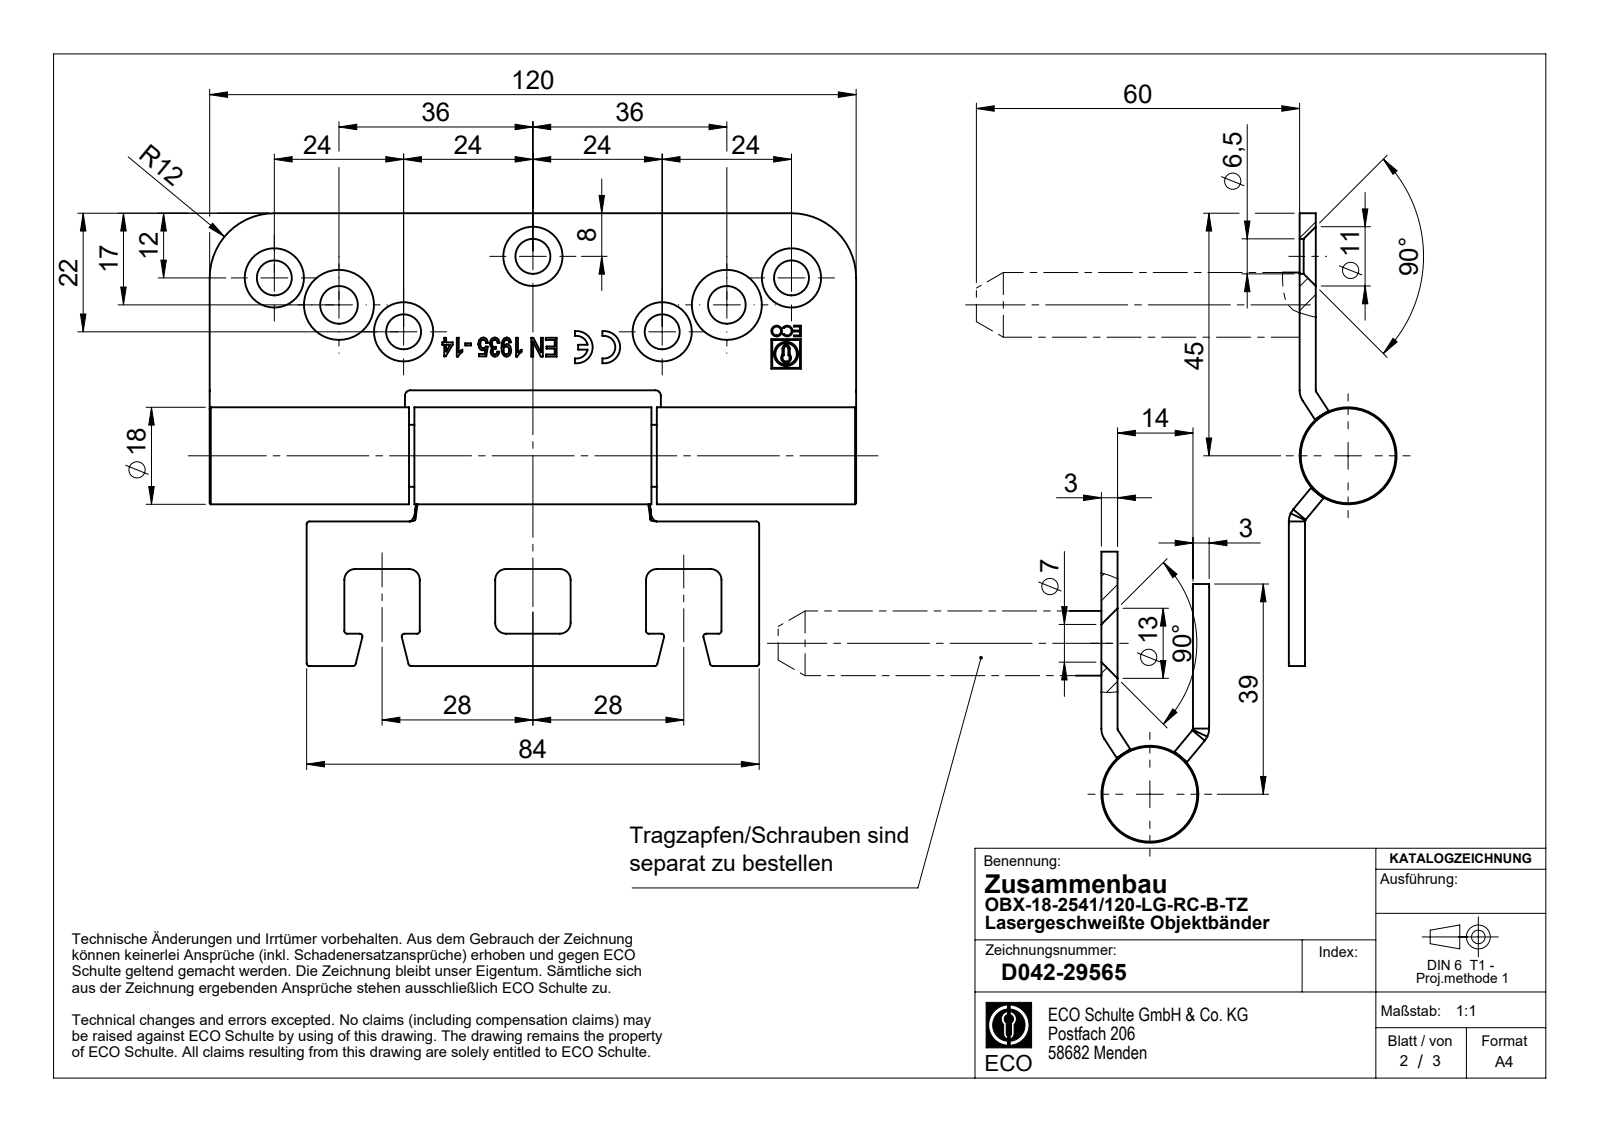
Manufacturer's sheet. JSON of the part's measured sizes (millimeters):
{"part_name": "B01572; B02853; D044-14308; DIN5401-III (+7 more)", "step_written_by": "SolidWorks 2017 (AUTOMOTIVE_DESIGN)", "units": "millimeters", "bodies": {"solids": 15, "faces": 524, "planar": 238, "cylindrical": 154, "other": 132}, "overall_size": [120, 80, 54], "volume_mm3": 60218, "surface_area_mm2": 35308, "round_holes": [[6.5, 5], [2, 2], [5, 2], [0.5, 1], [4.5, 1], [7.9, 1]], "round_bosses_or_shafts": [[12, 3], [6, 2], [18, 1], [11.8, 1], [11.5, 1], [7.7, 1], [4, 1], [1.65, 1]], "partial_cylinders_radius": [[0.5, 18], [2, 8], [0.25, 6], [0.68, 2], [1, 2], [2.1, 2], [3, 2], [3.5, 2]], "face_to_face_distances": [3, 17, 20, 14, 82, 11.5, 108.5, 1, 12, 6], "hole_center_spacings": [13, 26, 27.78, 37.11, 48.17, 60.21, 72.69, 84.15]}
